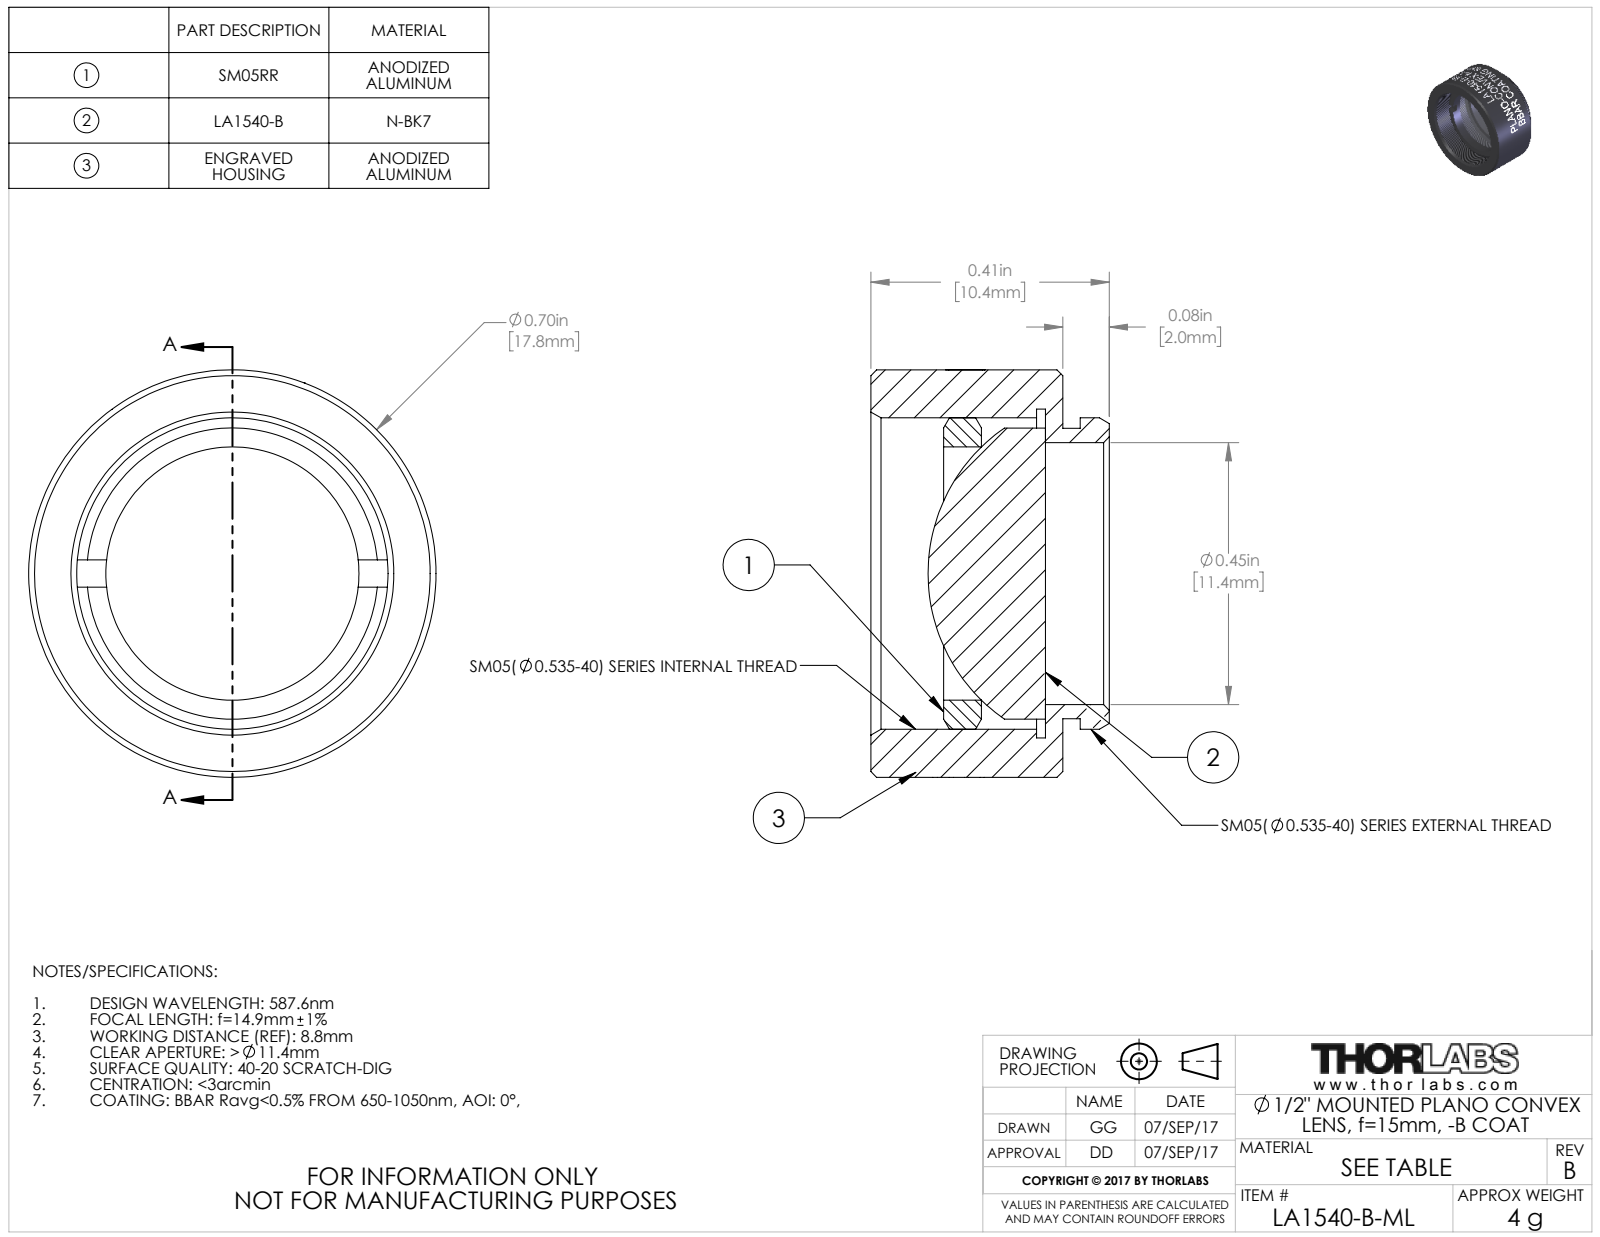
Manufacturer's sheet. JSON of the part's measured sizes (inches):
{"part_name": "24404-E0W", "step_written_by": "SolidWorks 2016 (CONFIG_CONTROL_DESIGN)", "units": "inches", "bodies": {"solids": 3, "faces": 278, "planar": 94, "cylindrical": 109, "other": 75}, "overall_size": [0.7, 0.7, 0.41], "volume_in3": 0.091, "surface_area_in2": 2.905, "round_holes": [[0.435, 1], [0.45, 1], [0.535, 1], [0.565, 1]], "round_bosses_or_shafts": [[0.7, 1], [0.535, 1], [0.5, 1], [0.499, 1]], "partial_cylinders_radius": [[0.35, 1]], "face_to_face_distances": [0.03, 0.3, 0.33, 0.125, 0.285, 0.14, 0.11, 0.19, 0.205, 0.175]}
